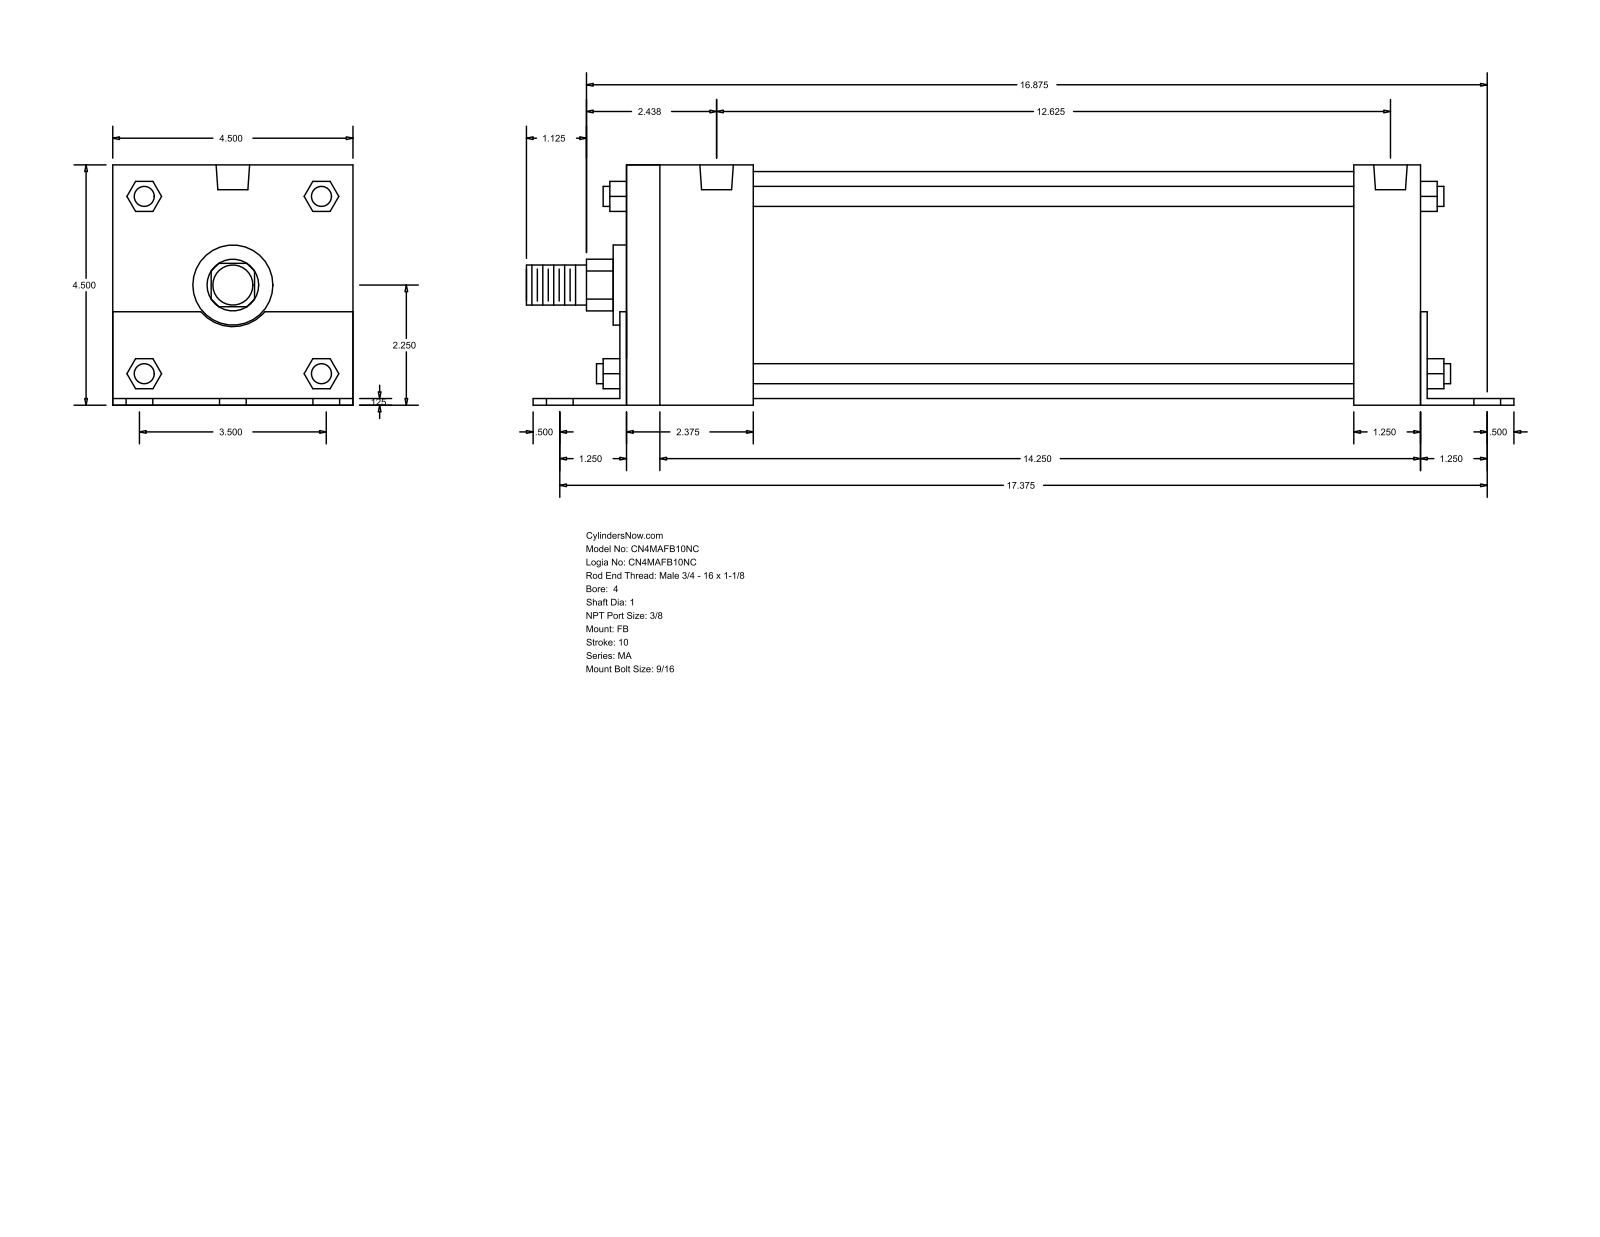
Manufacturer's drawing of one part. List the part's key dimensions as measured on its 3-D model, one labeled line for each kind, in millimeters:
Part name (STEP PRODUCT): MA_FB__0400_1
STEP written by: GSSL Pune (CONFIG_CONTROL_DESIGN)
Units: millimetres
Bodies: 0 solids, 140 faces (105 planar, 35 cylindrical, 0 other)
Overall size (bounding box): 469.9 × 114.35 × 114.3
Round holes (diameter × count): ⌀14.29 ×6, ⌀11.11 ×4, ⌀15.93 ×2
Round bosses / shafts (diameter × count): ⌀9.53 ×4, ⌀107.95 ×1, ⌀38.1 ×1, ⌀25.4 ×1, ⌀19.05 ×1
Partial cylindrical surfaces — rounded edges, fillets, slot ends (radius × count): R12.29 ×1, R19.81 ×1
Main face-to-face distances: 114.3, 3.17, 114.35, 381, 3.12, 111.18, 377.83, 384.17, 34.93, 349.24
Hole centre spacings: 44.45, 443.55, 441.32, 63.99, 67.5, 86.85, 88.9, 90.97
